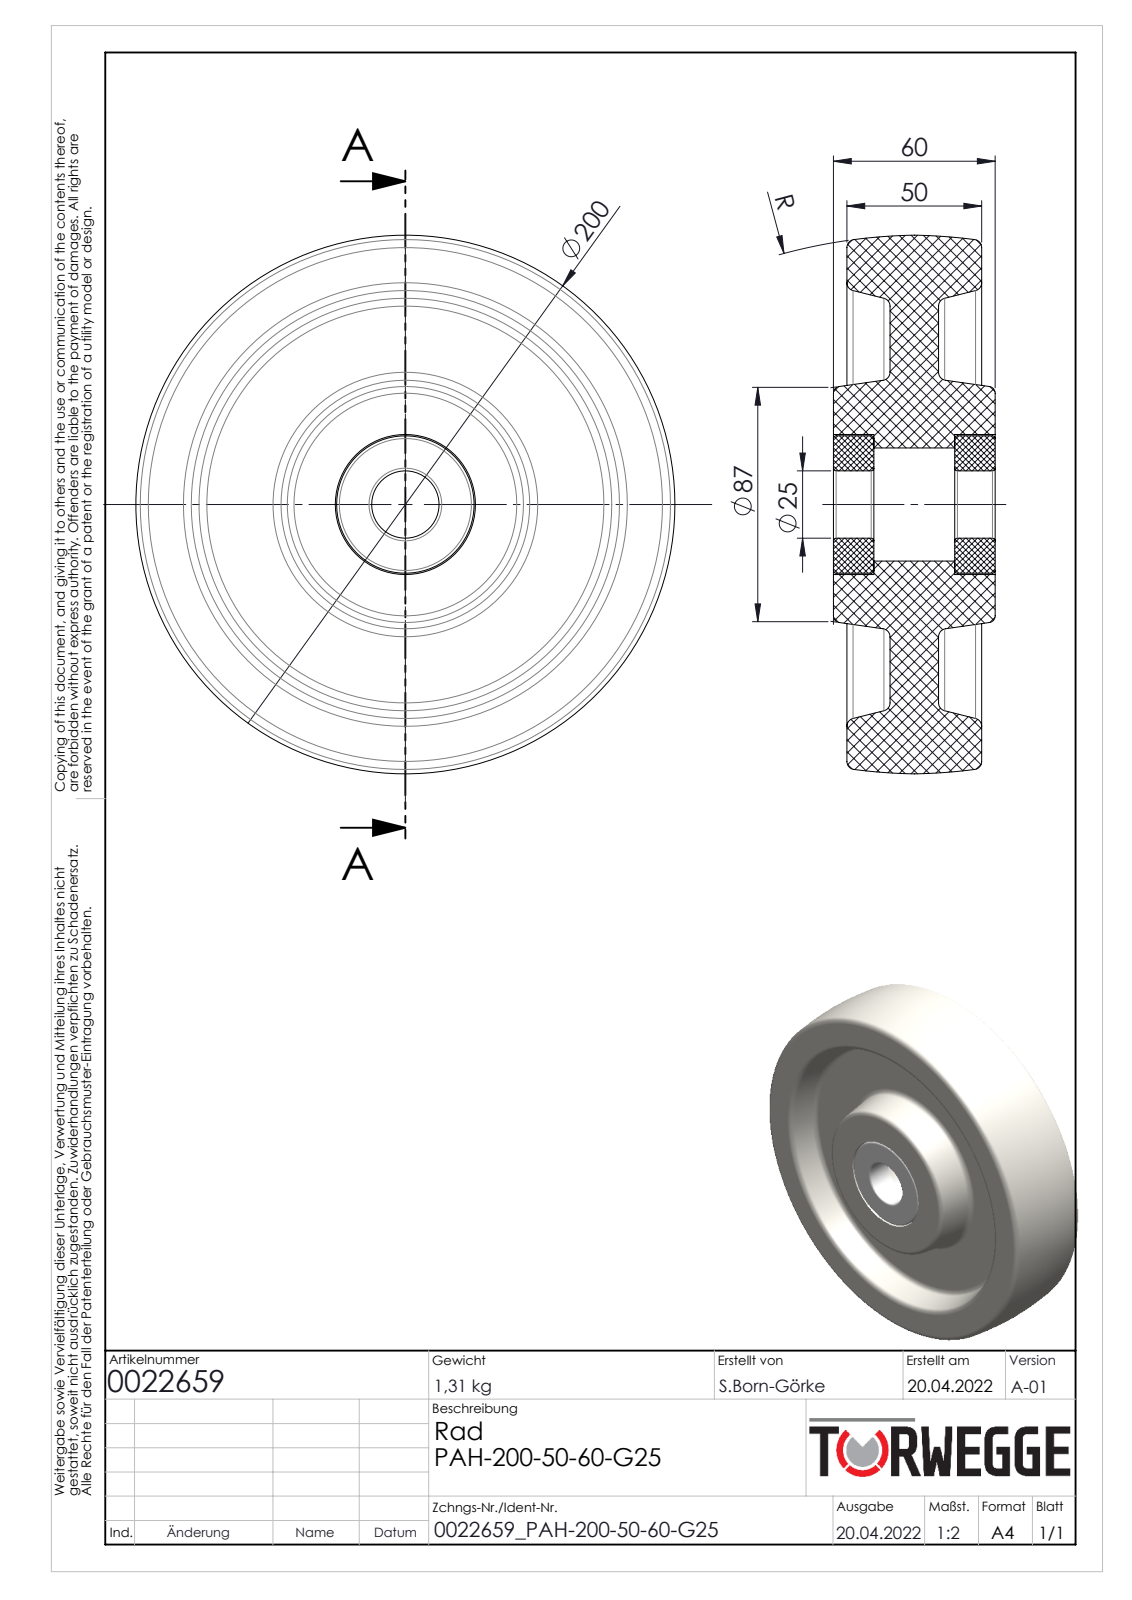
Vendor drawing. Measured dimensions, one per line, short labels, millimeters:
name: 0022659
written by: SolidWorks 2020 (AUTOMOTIVE_DESIGN)
unit: mm
bodies: 3 solids, 74 faces (12 planar, 14 cylindrical, 48 other)
size: 200 × 200 × 60
volume: 1 143 000 mm³; area: 129 750 mm²
holes: 1× ⌀25, 1× ⌀42, 1× ⌀52
bosses: 1× ⌀51
face distances: 16, 34, 18, 5, 21, 39, 55, 50, 60, 15
